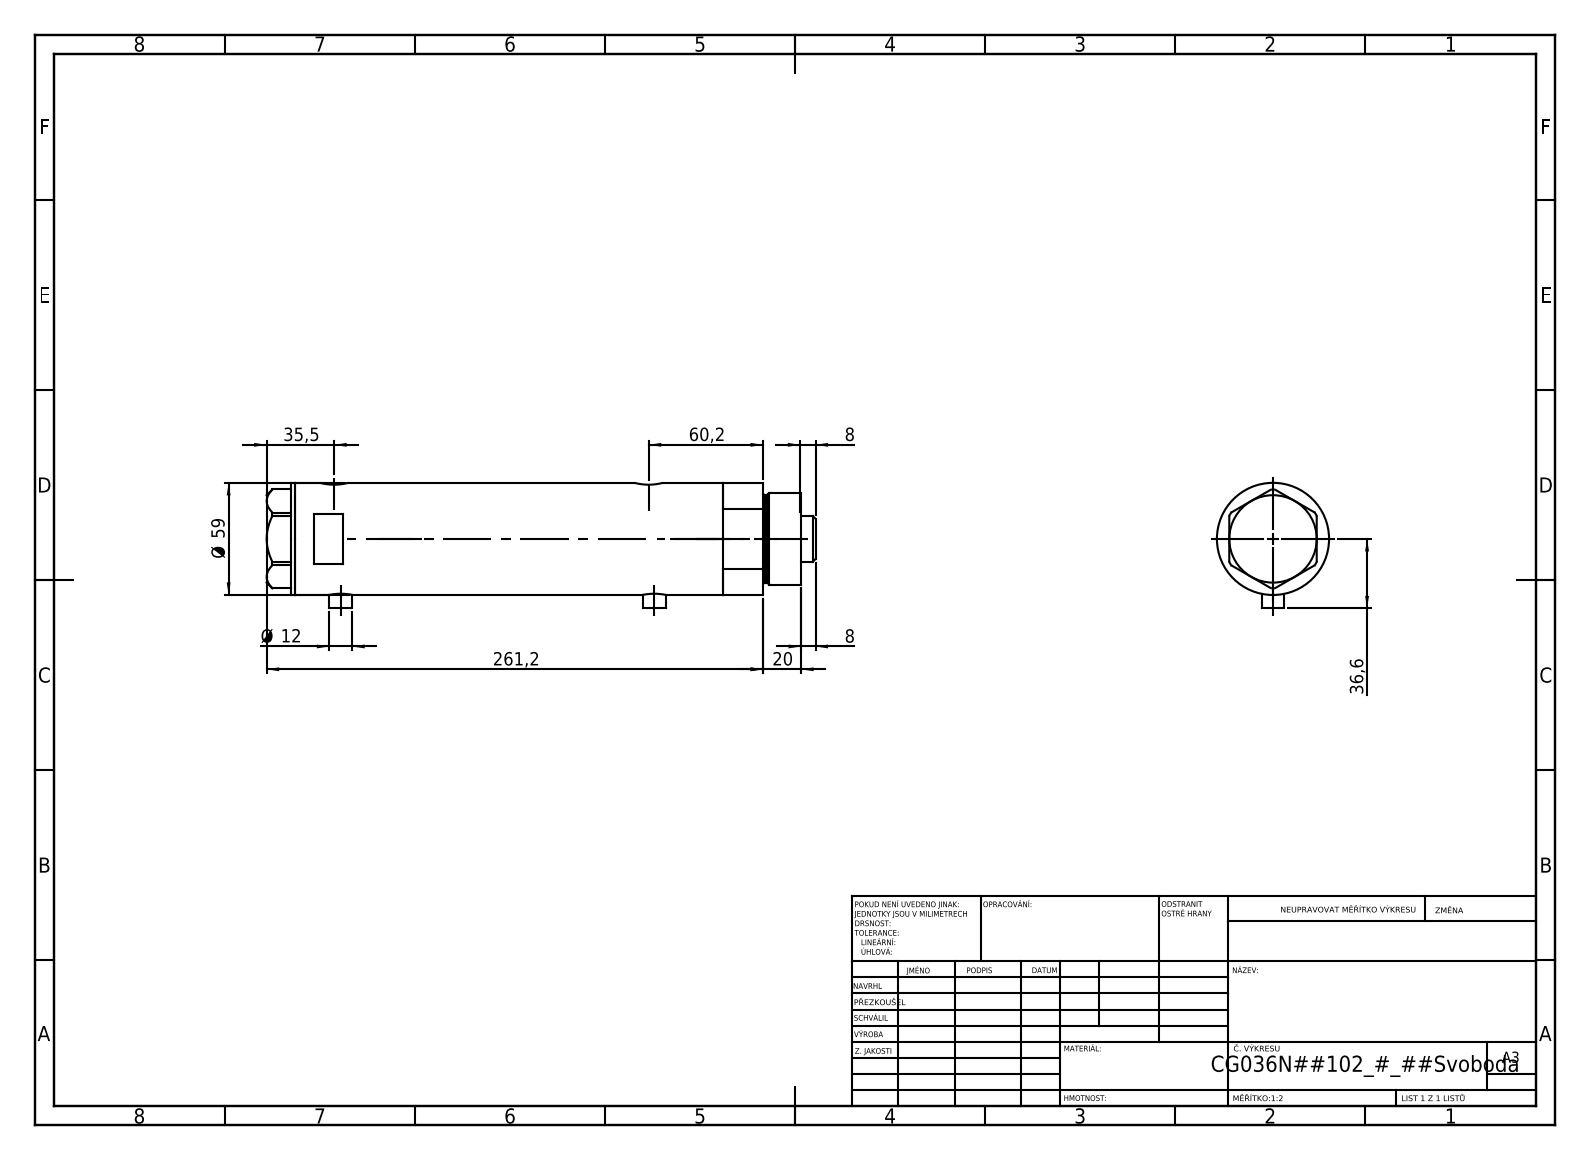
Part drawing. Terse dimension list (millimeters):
name: V270CG_MIDDLE; V270CG_BACK; V270CG_VC; V270CG_FRONT
written by: SolidWorks 2019 (CONFIG_CONTROL_DESIGN)
unit: mm
bodies: 4 solids, 126 faces (53 planar, 53 cylindrical, 20 other)
size: 288.8 × 66.1 × 59
volume: 678 217 mm³; area: 132 875 mm²
holes: 2× ⌀5, 2× ⌀9.73, 2× ⌀12.5, 2× ⌀15, 1× ⌀8.5, 1× ⌀25, 1× ⌀26.5, 1× ⌀36, 1× ⌀40, 1× ⌀52
bosses: 2× ⌀12, 1× ⌀59, 1× ⌀48, 1× ⌀46, 1× ⌀24
face distances: 187.2, 23.5, 163.7, 15, 38.5, 202.2, 2, 266.2, 281.2, 242.7
hole spacings: 2.9, 3.5, 162, 164.9, 165.5, 168.4
